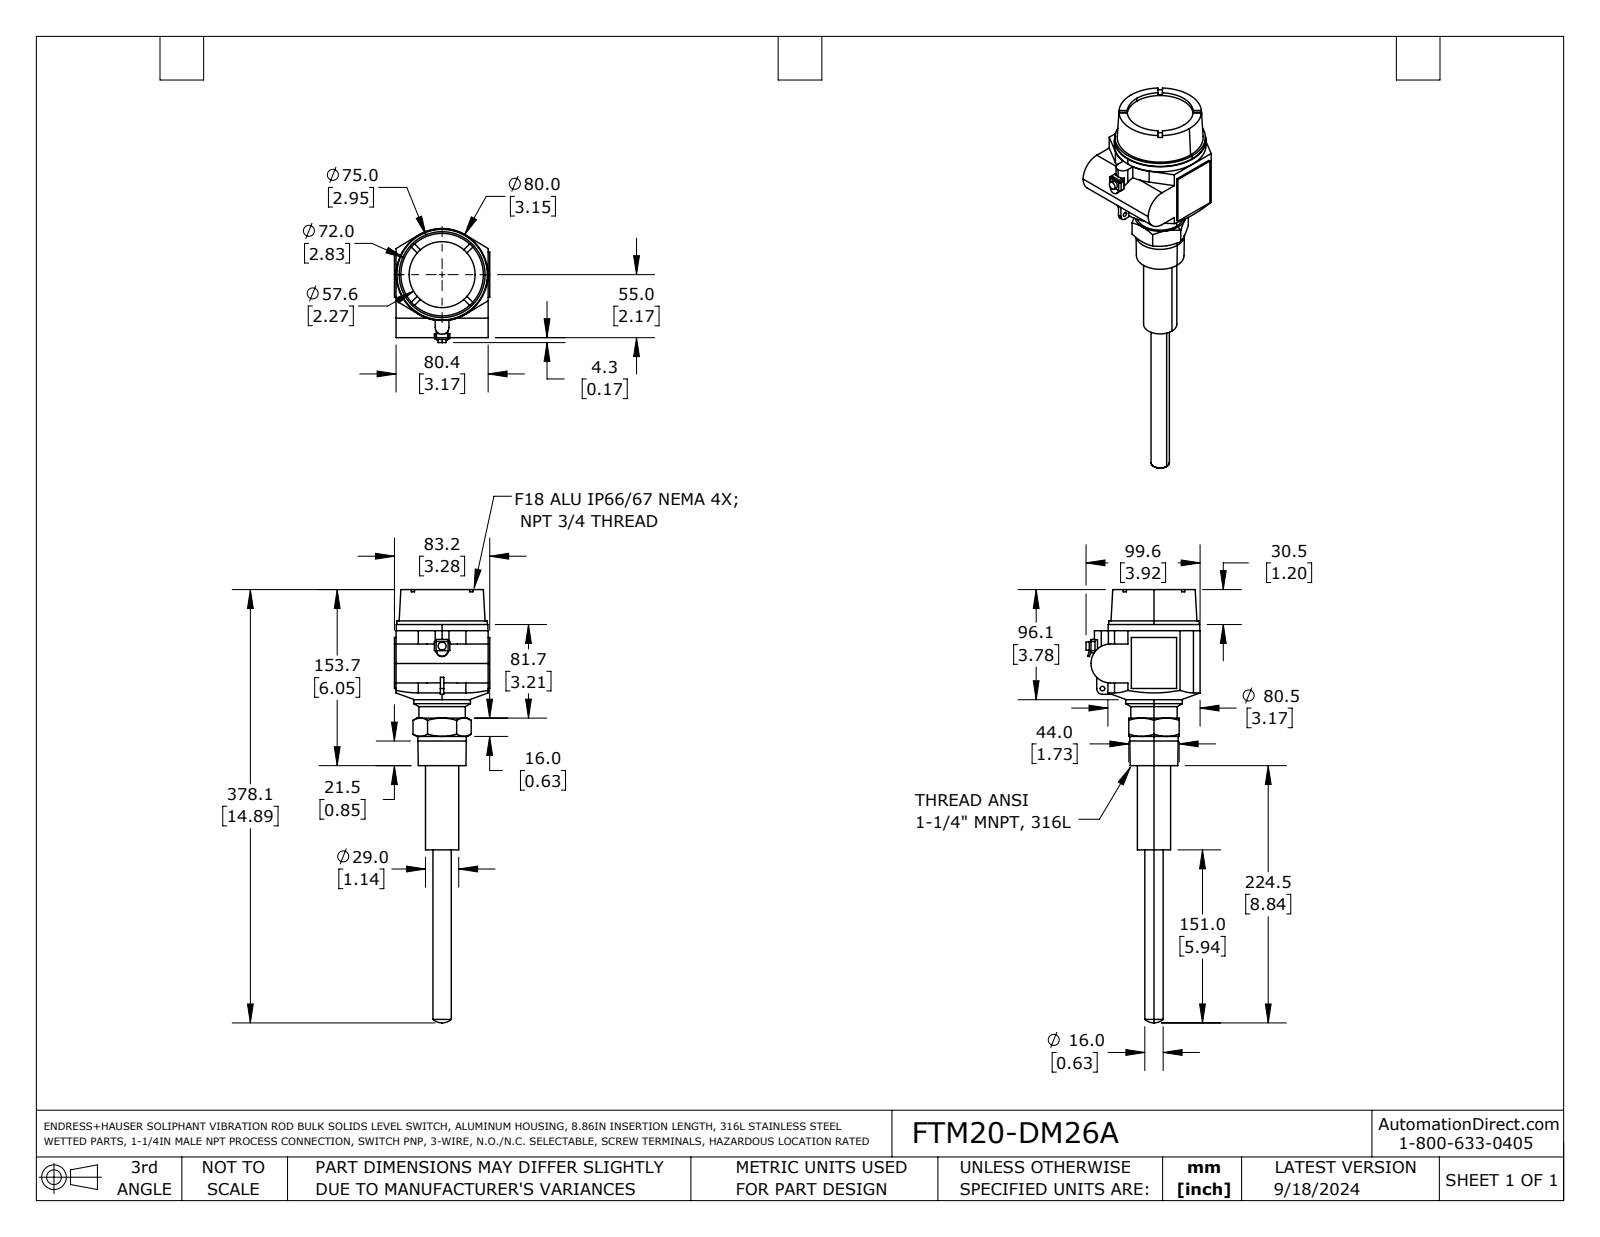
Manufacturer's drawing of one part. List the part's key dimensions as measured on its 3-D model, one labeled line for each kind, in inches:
Part name (STEP PRODUCT): FTM20-DM26A
STEP written by: SolidWorks 2021 (AUTOMOTIVE_DESIGN)
Units: inches
Bodies: 1 solid, 151 faces (88 planar, 36 cylindrical, 27 other)
Overall size (bounding box): 14.888 × 3.919 × 3.276
Volume: 41.75 in³ · Surface area: 96.75 in²
Round holes (diameter × count): ⌀0.157 ×1, ⌀2.268 ×1
Round bosses / shafts (diameter × count): ⌀3.15 ×1, ⌀3.11 ×1, ⌀1.949 ×1, ⌀1.661 ×1, ⌀1.594 ×1, ⌀1.142 ×1, ⌀0.63 ×1, ⌀0.276 ×1
Partial cylindrical surfaces — rounded edges, fillets, slot ends (radius × count): R0.059 ×3, R0.197 ×2, R0.236 ×1, R0.669 ×1, R1.585 ×1
Main face-to-face distances: 0.055, 3.22, 3.276, 3.165, 0.118, 1.732, 3.169, 5.931, 6.049, 4.636
